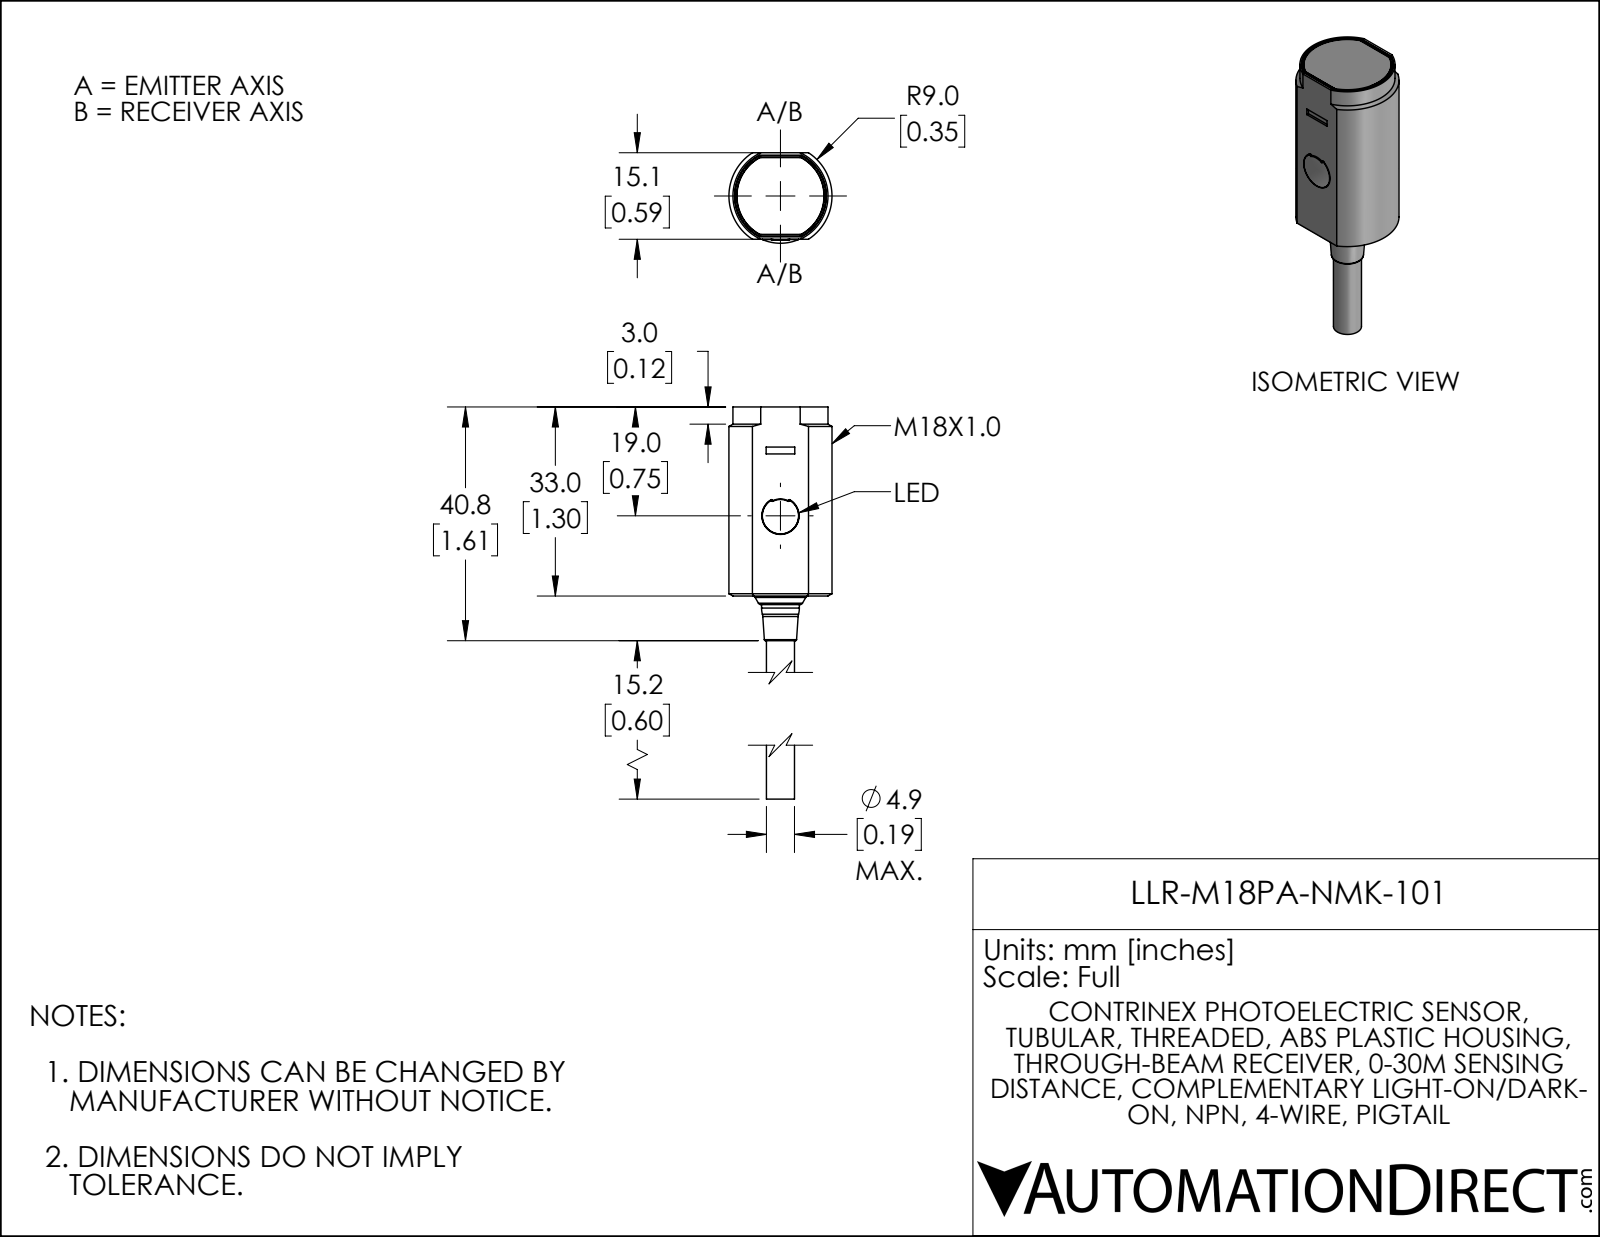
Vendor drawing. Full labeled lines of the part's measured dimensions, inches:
Part name (STEP PRODUCT): LLR-M18PA-NMK-101
STEP written by: SolidWorks 2021 (AUTOMOTIVE_DESIGN)
Units: inches
Bodies: 1 solid, 93 faces (39 planar, 41 cylindrical, 13 other)
Overall size (bounding box): 2.205 × 0.709 × 0.622
Volume: 0.501 in³ · Surface area: 4.23 in²
Round holes (diameter × count): ⌀0.256 ×1
Round bosses / shafts (diameter × count): ⌀0.26 ×1, ⌀0.193 ×1
Partial cylindrical surfaces — rounded edges, fillets, slot ends (radius × count): R0.006 ×8, R0.014 ×8, R0.028 ×8, R0.112 ×1, R0.116 ×1, R0.299 ×1, R0.302 ×1, R0.313 ×1
Main face-to-face distances: 0.594, 1.297, 1.299, 0.016, 2.205, 2.203, 0.906, 0.579, 0.014, 0.563
